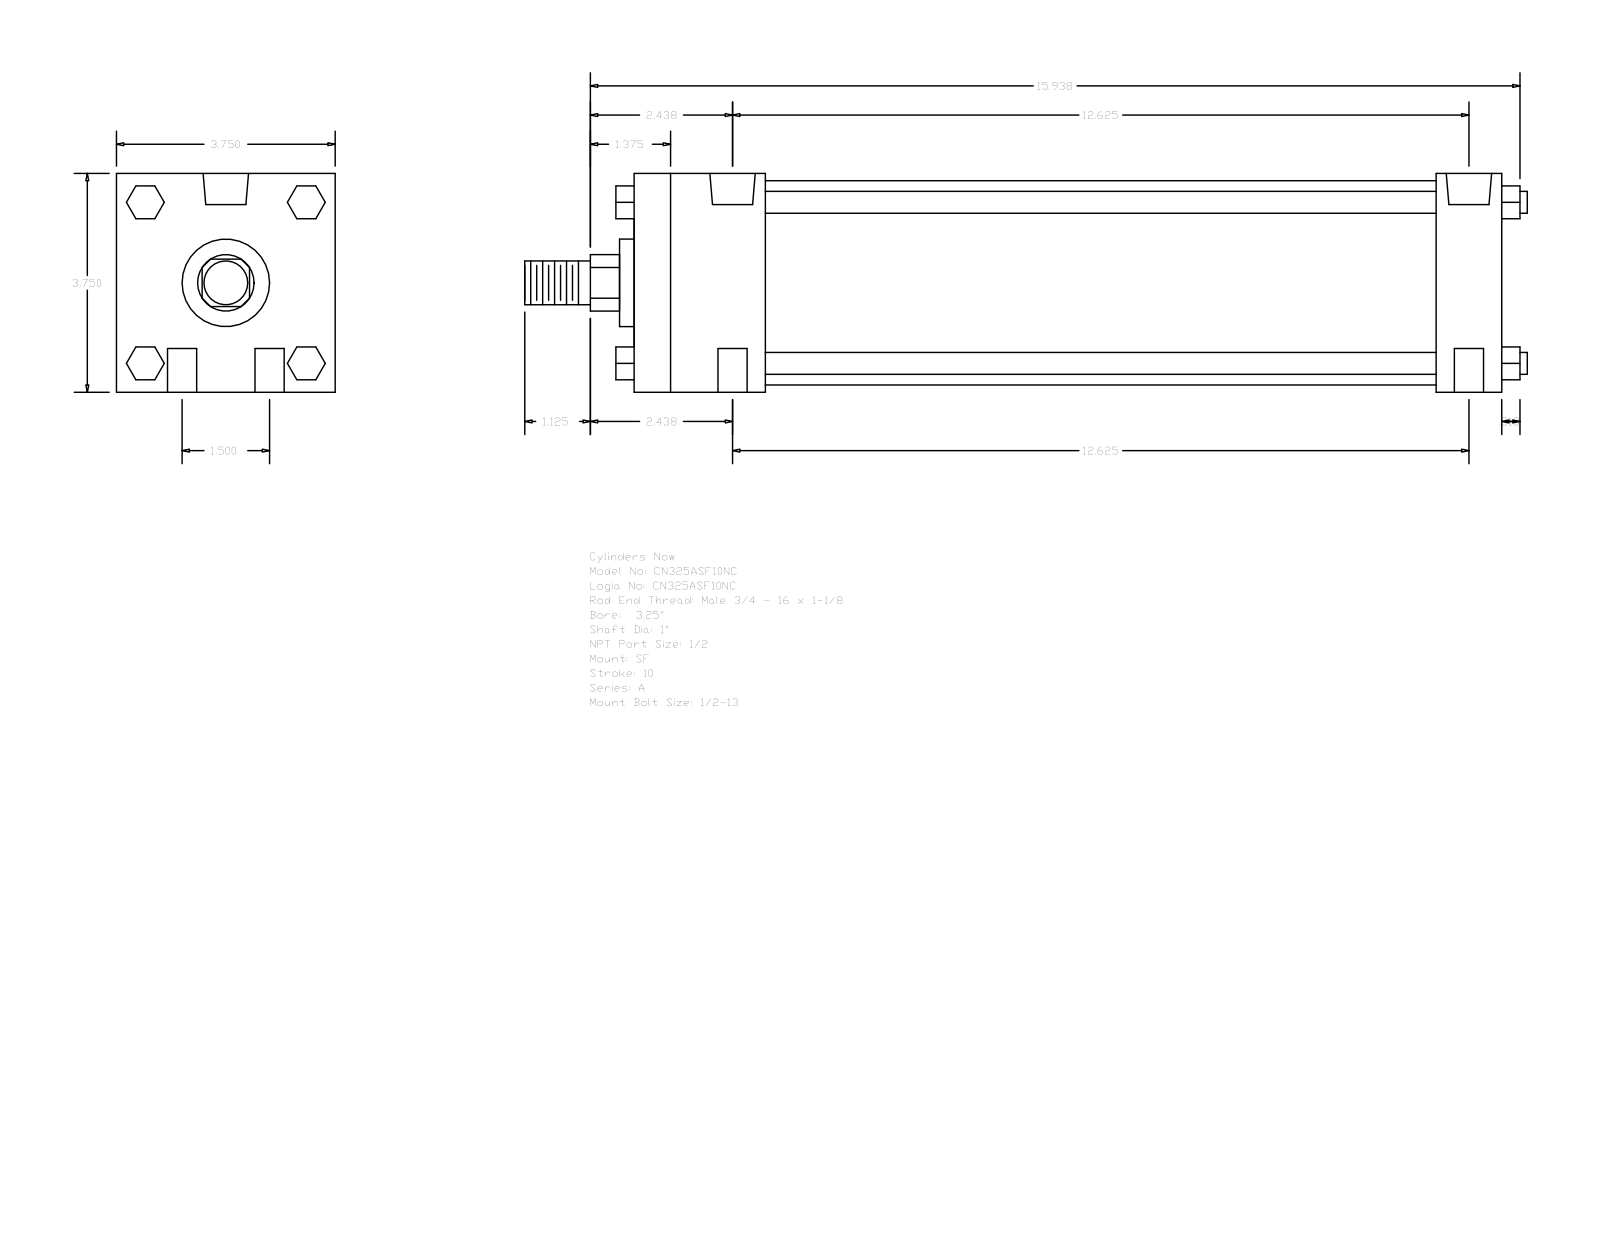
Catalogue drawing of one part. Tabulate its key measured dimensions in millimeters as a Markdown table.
| quantity | value |
| --- | --- |
| part name | A_SF__0325_1 |
| STEP written by | GSSL Pune (CONFIG_CONTROL_DESIGN) |
| units | millimeters |
| bodies | 0 solids, 124 faces (94 planar, 30 cylindrical, 0 other) |
| overall size | 436.56 × 95.25 × 95.25 |
| round holes (diameter × count) | 12.7 × 4, 8.73 × 2, 19.77 × 2 |
| round bosses / shafts (diameter × count) | 9.53 × 4, 88.9 × 1, 38.1 × 1, 25.4 × 1, 19.05 × 1 |
| partial cylindrical surfaces (radius × count) | 12.29 × 1 |
| main face-to-face distances | 95.24, 377.83, 349.25, 28.58, 57.15, 292.1, 320.68, 14.28, 35.05, 60.71 |
| hole center spacings | 19.05, 321.25, 320.68, 38.1, 322.94, 314.32 |
